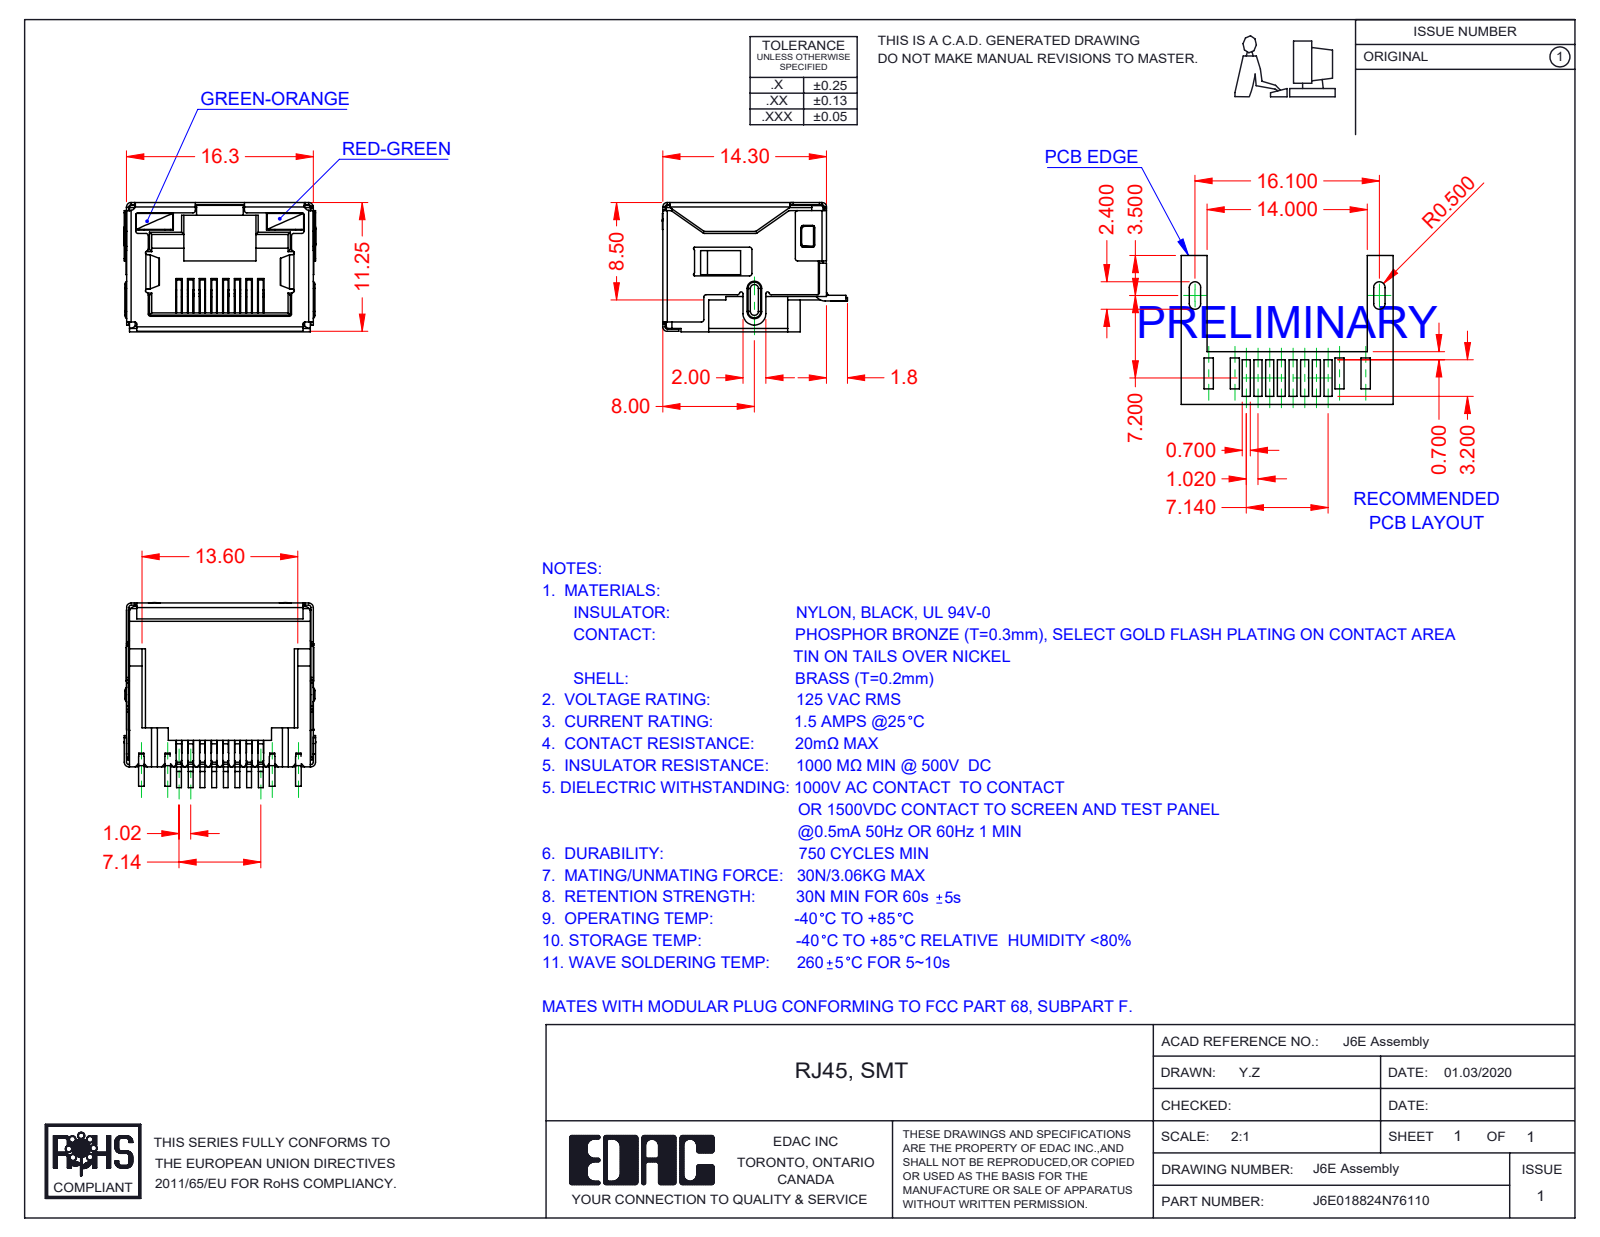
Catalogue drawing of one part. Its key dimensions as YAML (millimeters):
part_name: "6E LED RH_6-Red-Green; 6E LED LH_7-Green-Orange; 6E Shield_LED; J6E018824N76110 (+2 more)"
step_written_by: "SolidWorks 2016 (CONFIG_CONTROL_DESIGN)"
units: millimeters
bodies: {solids: 12, faces: 1500, planar: 1099, cylindrical: 351, other: 50}
overall_size: [16.75, 16.15, 11.3]
volume: 1109
surface_area: 4045
partial_cylinders:
  - {radius: 0.2, count: 82}
  - {radius: 0.25, count: 17}
  - {radius: 0.4, count: 13}
  - {radius: 0.5, count: 13}
  - {radius: 0.1, count: 10}
  - {radius: 0.15, count: 7}
  - {radius: 0.3, count: 4}
  - {radius: 1, count: 3}
face_to_face_distances: [11.05, 16.05, 16.1, 15.85, 11.1, 11.3, 2.4, 0.7, 9.85, 0.49]
